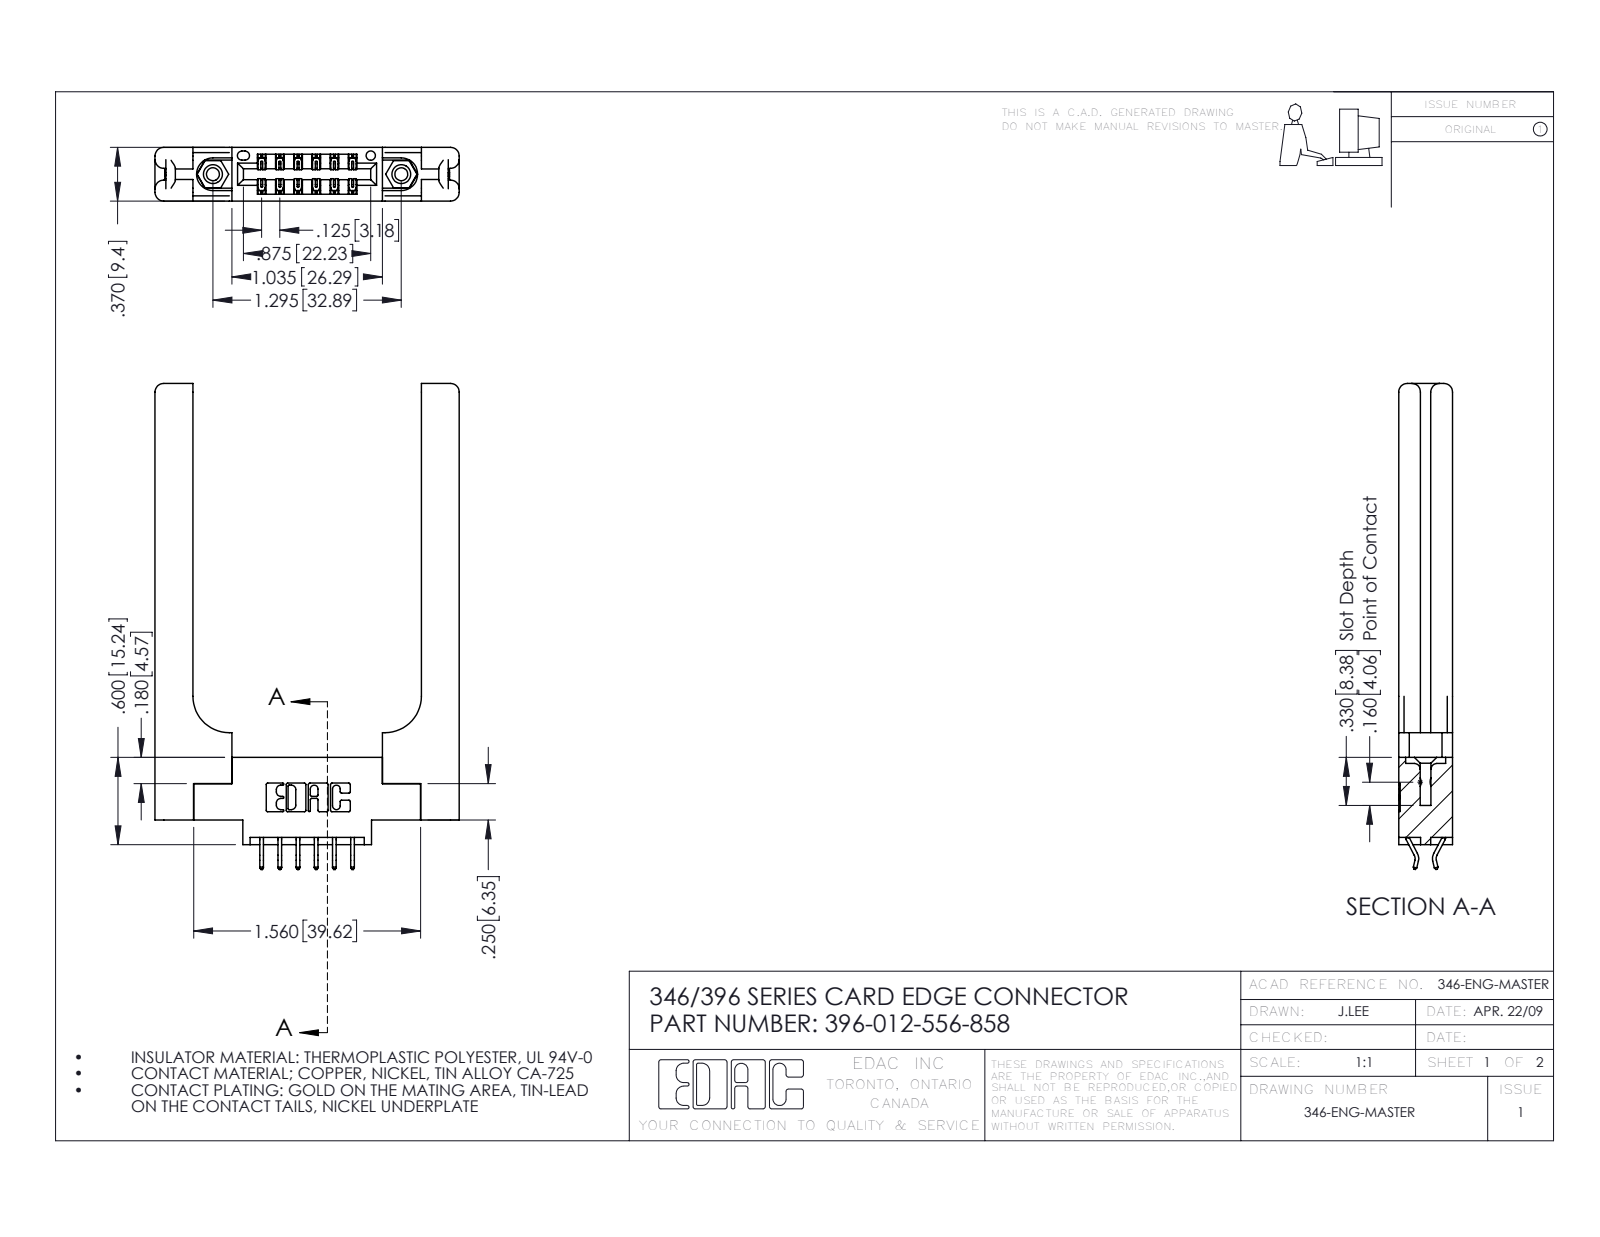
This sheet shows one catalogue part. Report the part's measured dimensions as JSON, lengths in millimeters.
{"part_name": "345-292-001_556 Tail; 346-220-058_345-220-058; 345-250-001_345-250-001-102; 396-012-556-858 (+1 more)", "step_written_by": "SolidWorks 2016 (CONFIG_CONTROL_DESIGN)", "units": "millimeters", "bodies": {"solids": 17, "faces": 1078, "planar": 696, "cylindrical": 322, "other": 60}, "overall_size": [84.8, 53.1, 9.4], "volume_mm3": 12200, "surface_area_mm2": 11100, "round_holes": [[2.3, 2], [3.2, 2], [4, 2], [1.6, 1]], "round_bosses_or_shafts": [[3.9, 2]], "partial_cylinders_radius": [[0.3, 22], [0.2, 18], [1.5, 16], [0.2, 6], [0.8, 6], [0.7, 3], [0.3, 2], [0.4, 2]], "face_to_face_distances": [9.4, 3.8, 5.6, 1.8, 6.4, 3.8, 39.9, 2.6, 1.2, 8.2], "hole_center_spacings": [6.2, 27.7, 32.9]}
